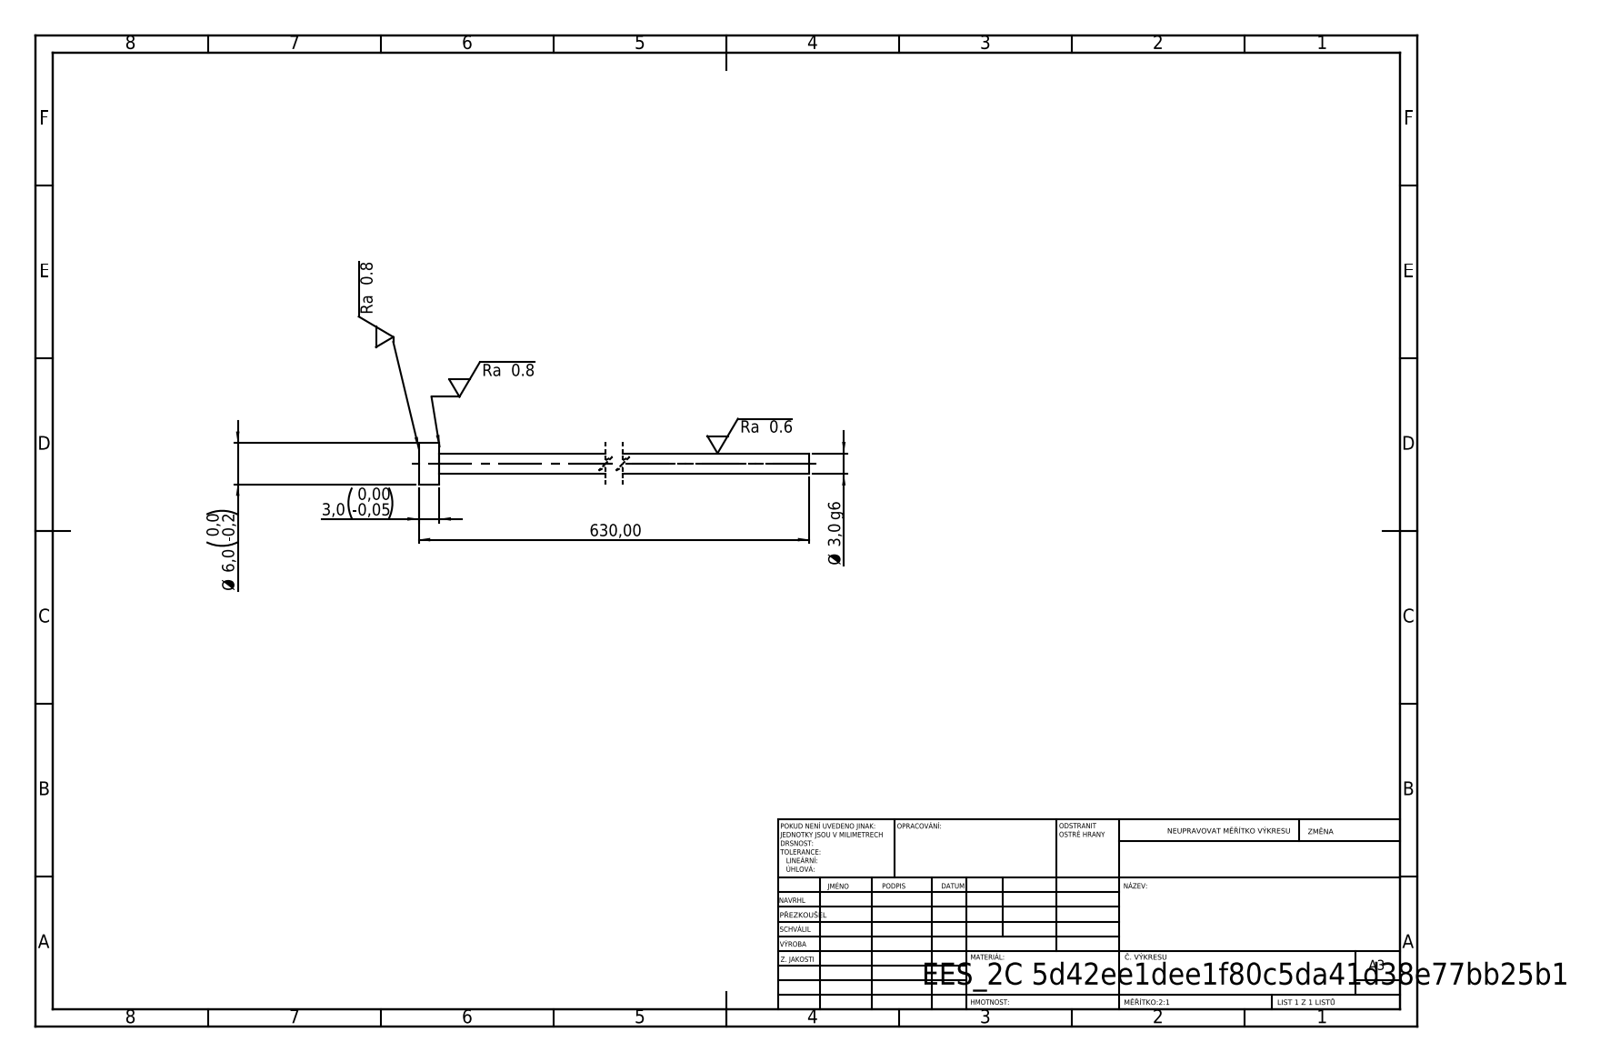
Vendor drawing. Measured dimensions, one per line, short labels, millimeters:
written by: SolidWorks 2019 (CONFIG_CONTROL_DESIGN)
unit: mm
bodies: 1 solid, 7 faces (3 planar, 4 cylindrical, 0 other)
size: 630 × 6 × 6
volume: 4 517 mm³; area: 6 022 mm²
bosses: 1× ⌀6, 1× ⌀3
face distances: 3, 630, 627
